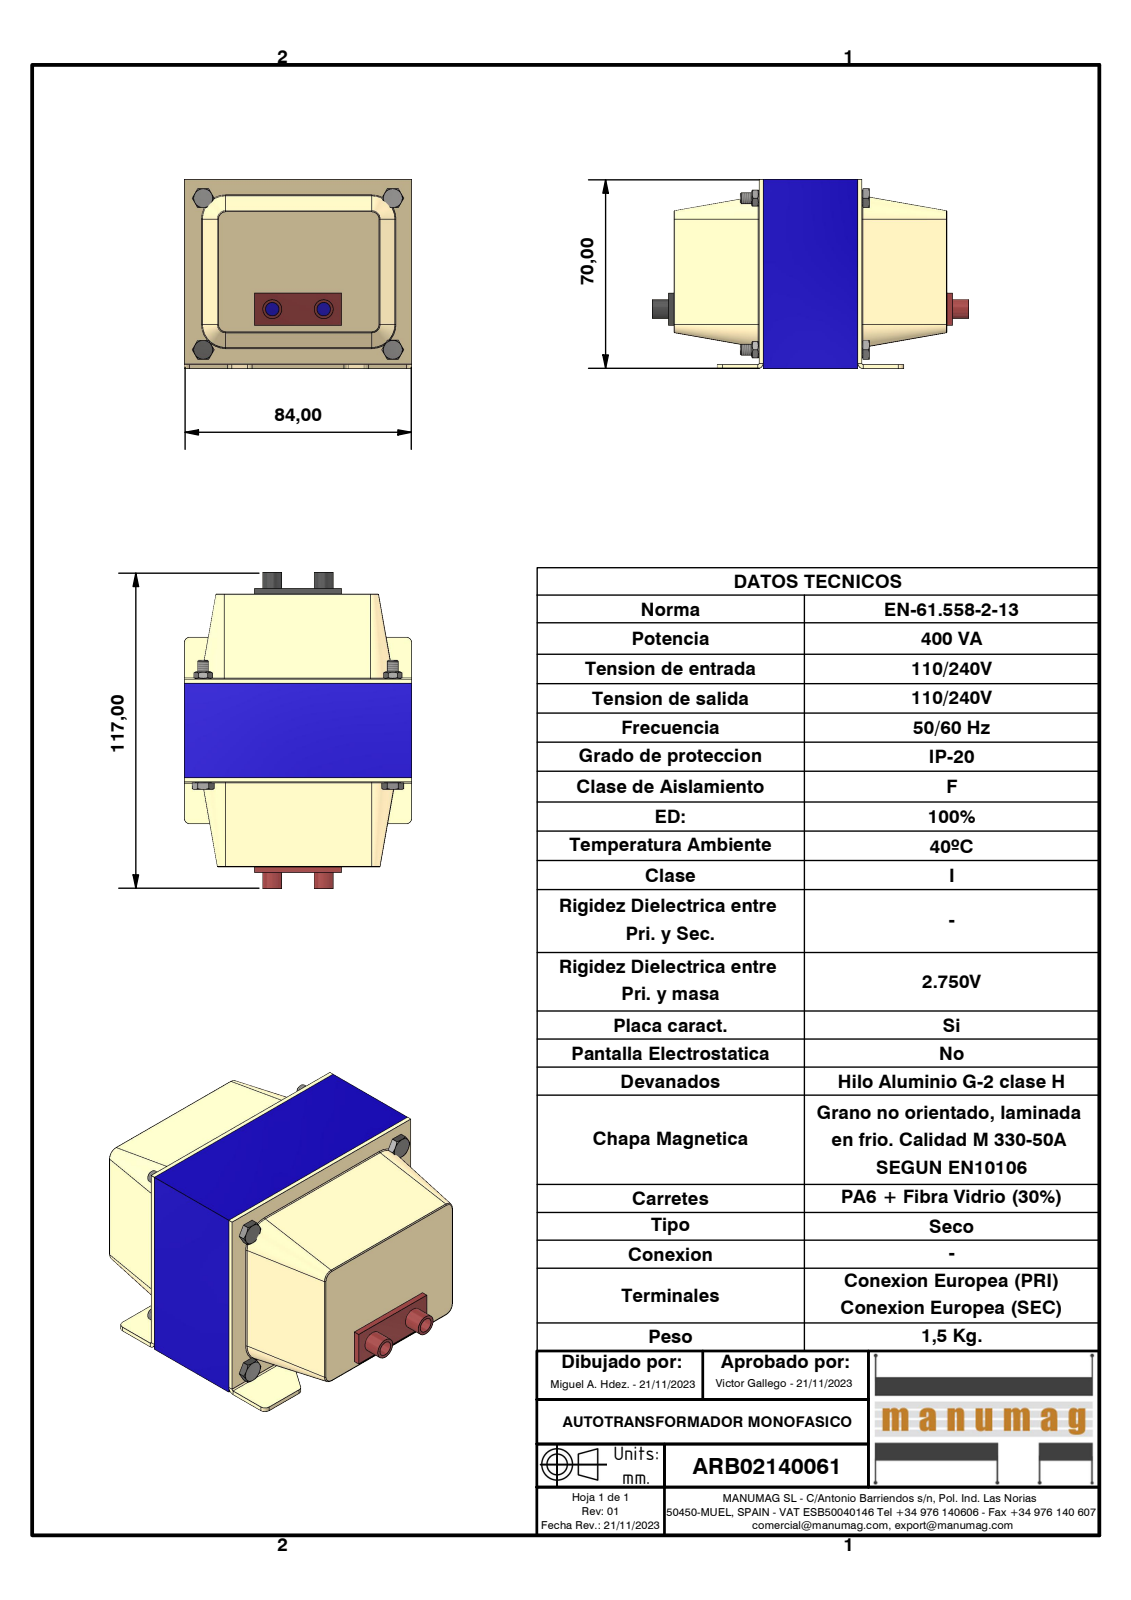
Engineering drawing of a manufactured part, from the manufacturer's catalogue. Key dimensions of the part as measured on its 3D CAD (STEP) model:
Part name (STEP PRODUCT): ARB02140061; EI84 x 70 - 35 (RC28) Azul; TAPA RC28 RECEPTACULO; Receptaculo Rojo (+3 more)
STEP written by: Autodesk Inventor 2023 (AUTOMOTIVE_DESIGN)
Units: millimetres
Bodies: 13 solids, 310 faces (162 planar, 68 cylindrical, 80 other)
Overall size (bounding box): 117 × 84 × 70
Volume: 186 006 mm³ · Surface area: 85 894 mm²
Round holes (diameter × count): ⌀4 ×8, ⌀2.85 ×4, ⌀4.5 ×4, ⌀5 ×2
Round bosses / shafts (diameter × count): ⌀5.9 ×4, ⌀3.62 ×4, ⌀7 ×2
Partial cylindrical surfaces — rounded edges, fillets, slot ends (radius × count): R0.38 ×16, R2 ×14, R0.5 ×2
Main face-to-face distances: 1.5, 68, 31.5, 14, 35, 61.64, 70, 56, 33, 28
Hole centre spacings: 70, 89.64, 46.96, 56, 29.58, 29.59, 48.27, 48.28
